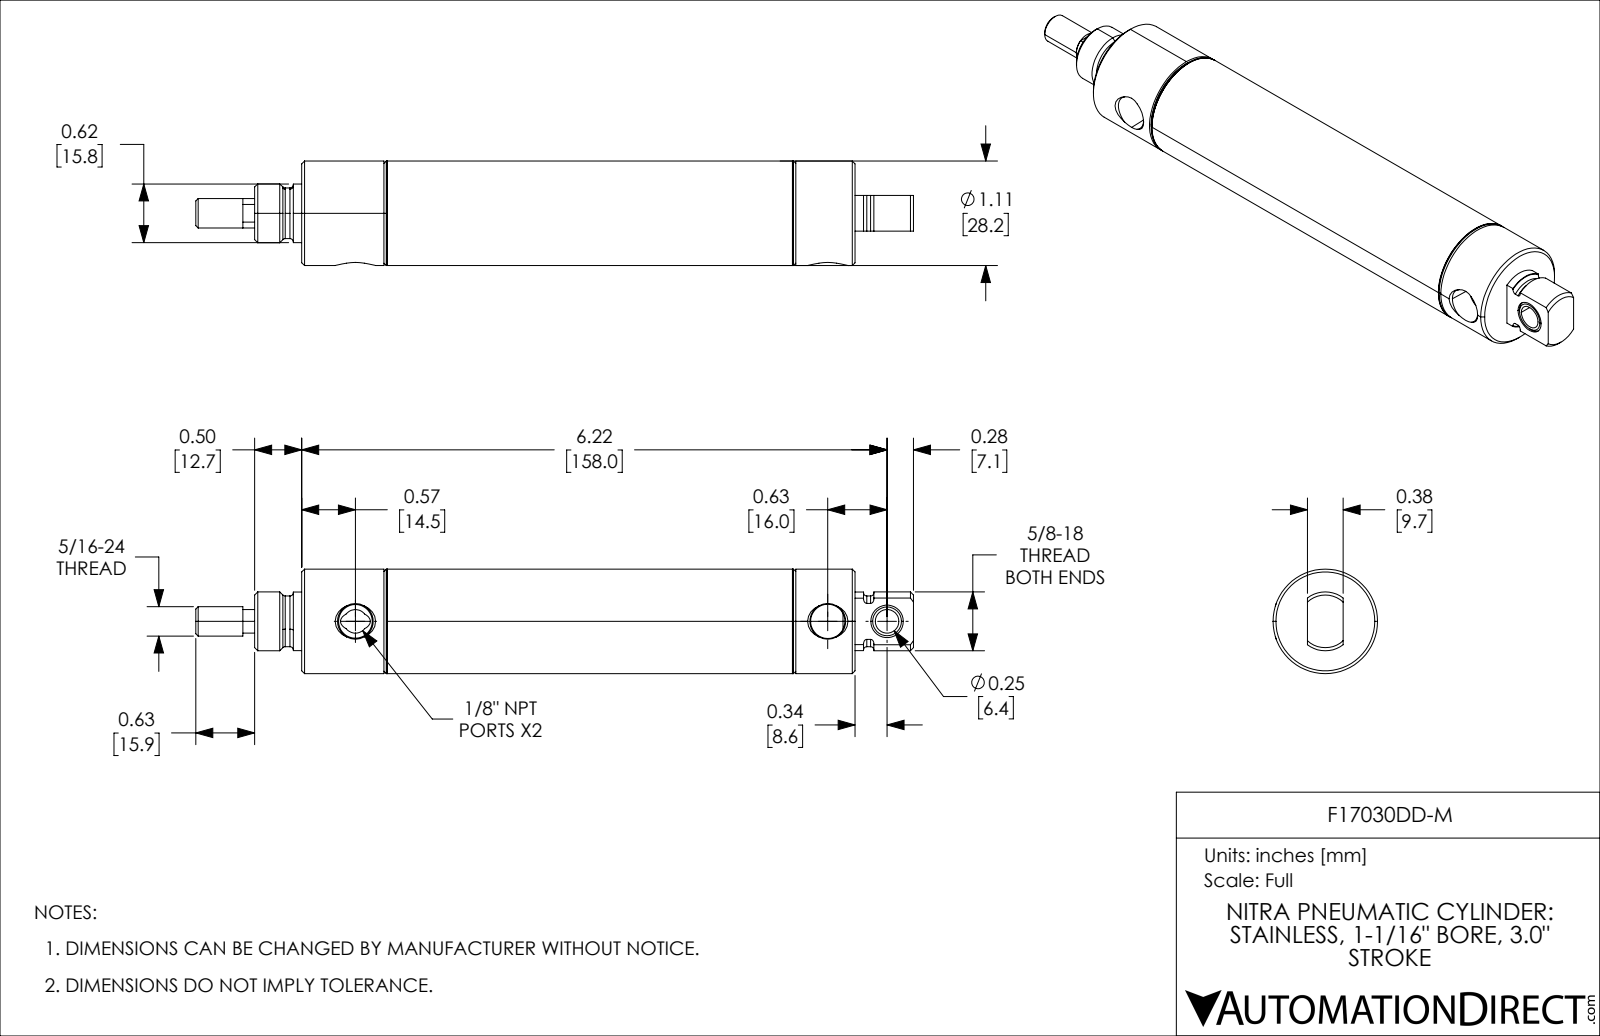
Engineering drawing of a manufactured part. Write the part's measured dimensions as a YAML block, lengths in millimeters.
part_name: "F17030DD-M_7; F17030DD-M_5; F17030DD-M_11; F17030DD-M (+2 more)"
step_written_by: "SolidWorks 2021 (CONFIG_CONTROL_DESIGN)"
units: millimeters
bodies: {solids: 5, faces: 156, planar: 30, cylindrical: 58, other: 68}
overall_size: [193.68, 28.19, 28.19]
volume: 52813
surface_area: 37305
round_holes:
  - {diameter: 6.38, count: 1}
  - {diameter: 8.53, count: 1}
  - {diameter: 8.78, count: 1}
  - {diameter: 9.25, count: 1}
  - {diameter: 9.53, count: 1}
  - {diameter: 19.05, count: 1}
  - {diameter: 25.7, count: 1}
round_bosses_or_shafts:
  - {diameter: 28.19, count: 1}
  - {diameter: 27.23, count: 1}
  - {diameter: 15.88, count: 1}
  - {diameter: 15.81, count: 1}
  - {diameter: 13.68, count: 1}
  - {diameter: 7.94, count: 1}
  - {diameter: 7.92, count: 1}
partial_cylinders:
  - {radius: 3.17, count: 1}
  - {radius: 6.84, count: 1}
face_to_face_distances: [22.22, 76.2, 98.42, 120.75, 44.55, 22.33, 28.58, 104.78, 127, 149.33]
hole_center_spacings: [16.01]
